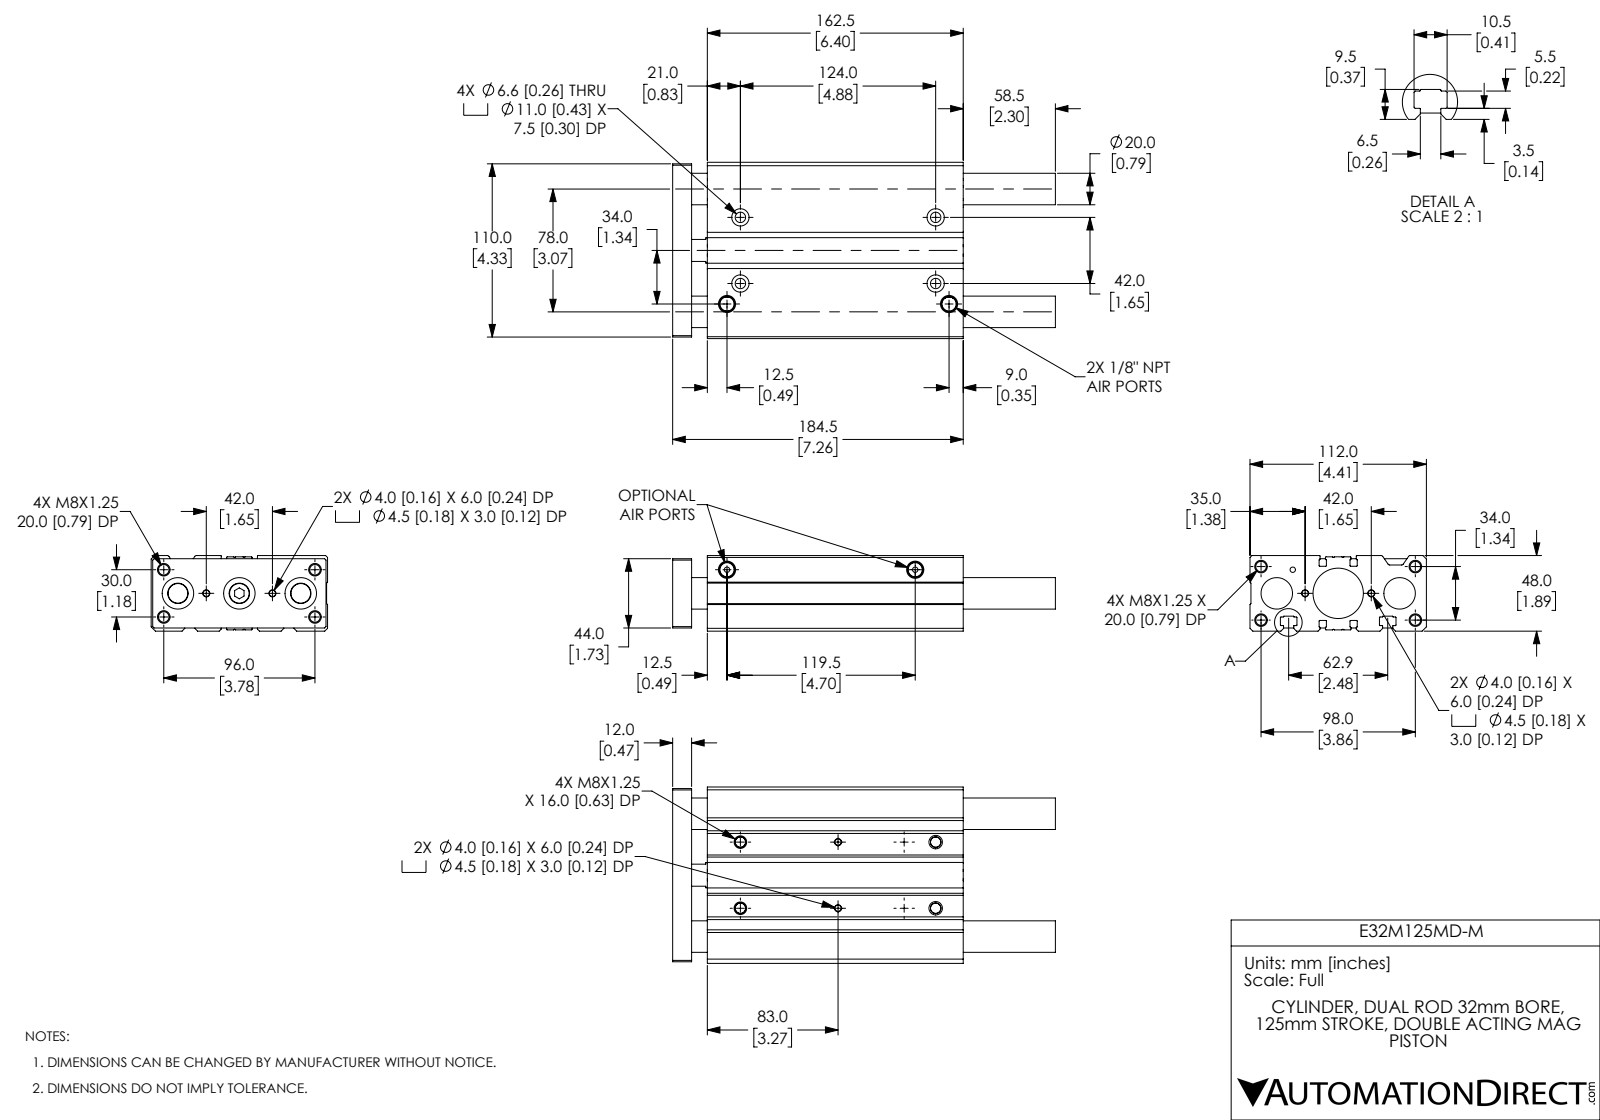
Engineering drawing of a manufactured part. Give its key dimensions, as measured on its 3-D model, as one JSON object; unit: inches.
{"part_name": "E32M125MD-M_BODY; E32M125MD-M_ENDPLATE; E32M125MD-M", "step_written_by": "SolidWorks 2019 (CONFIG_CONTROL_DESIGN)", "units": "inches", "bodies": {"solids": 5, "faces": 423, "planar": 139, "cylindrical": 190, "other": 94}, "overall_size": [9.567, 4.409, 1.89], "volume_in3": 49.66, "surface_area_in2": 282, "round_holes": [[0.262, 11], [0.157, 4], [0.177, 4], [0.26, 4], [0.433, 4], [0.394, 3], [0.787, 3], [0.135, 2], [0.51, 2], [0.135, 1], [0.262, 1], [0.787, 1]], "round_bosses_or_shafts": [[0.63, 1], [0.51, 1]], "partial_cylinders_radius": [[0.008, 32], [0.016, 28], [0.047, 4], [0.012, 2]], "face_to_face_distances": [1.89, 0.236, 0.031, 4.409, 1.858, 0.866, 1.484, 1.622, 0.472, 0.394], "hole_center_spacings": [0.088, 0.689, 0.776, 1.216, 1.261, 1.29, 1.654, 1.98]}
